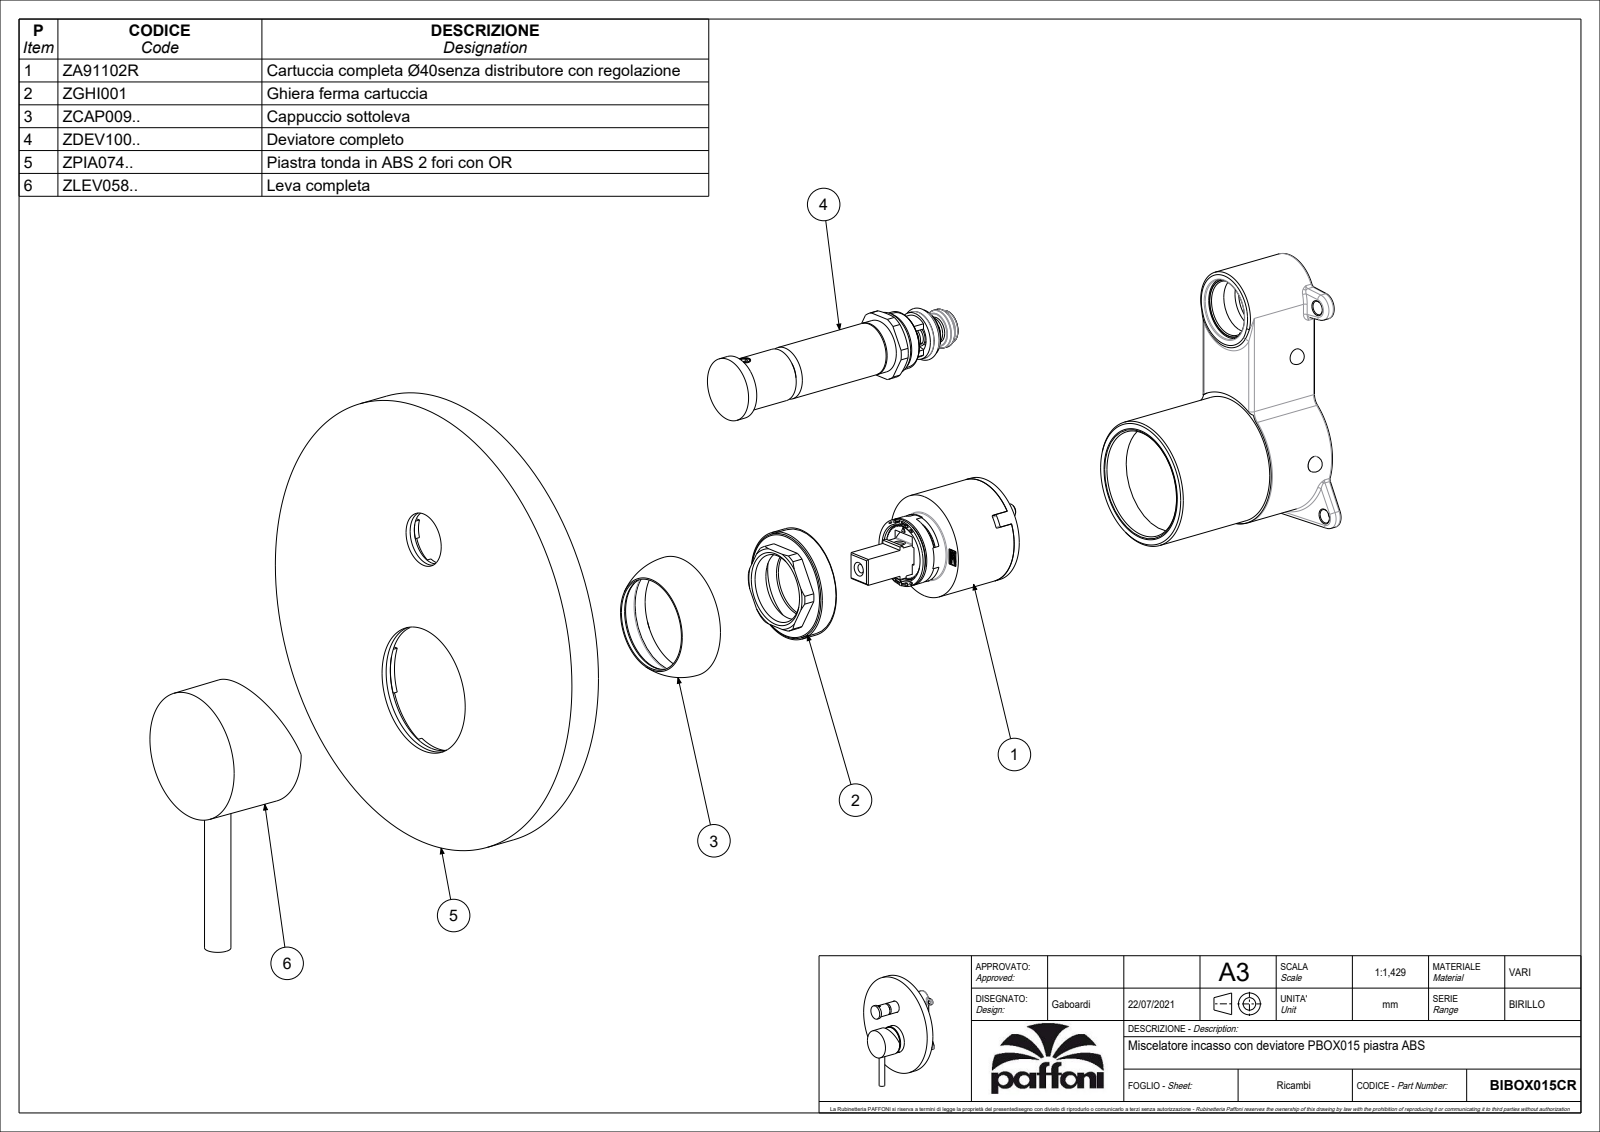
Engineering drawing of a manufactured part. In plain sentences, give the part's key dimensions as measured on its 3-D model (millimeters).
The part is named "BIBOX015CR". Its 3-D file was written by "CREO PARAMETRIC BY PTC INC, 2020044 (CONFIG_CONTROL_DESIGN)". It is 5 solids with 879 faces: 522 planar, 222 cylindrical and 135 other. Overall it measures 191.47 by 173 by 59.21 millimeters. Its volume is 234 037 cubic millimeters and its surface area 121 503 square millimeters. Round holes: 3 of diameter 3.3, 1 of diameter 3, 1 of diameter 4, 1 of diameter 4.2, 1 of diameter 5, 1 of diameter 7.1, 1 of diameter 10, 1 of diameter 16, 1 of diameter 18.2, 1 of diameter 20.5, 1 of diameter 21, 1 of diameter 21.2. Round bosses or shafts: 1 of diameter 173, 1 of diameter 167, 1 of diameter 57, 1 of diameter 48.1, 1 of diameter 39.5, 1 of diameter 33, 1 of diameter 29, 1 of diameter 25.8. Partial cylindrical surfaces (rounded edges, fillets, slot ends): 24 of radius 0.2, 2 of radius 6.5, 1 of radius 0.5, 1 of radius 7, 1 of radius 10.05, 1 of radius 10.75, 1 of radius 11.9, 1 of radius 12.3. The main face-to-face distances are 13, 2, 11, 6.5, 40.8, 15, 38.8, 4.5, 8.5, 11.9. The hole center spacings are 1.62, 13.8, 25.75, 27.37, 34.25, 60, 61.62.
